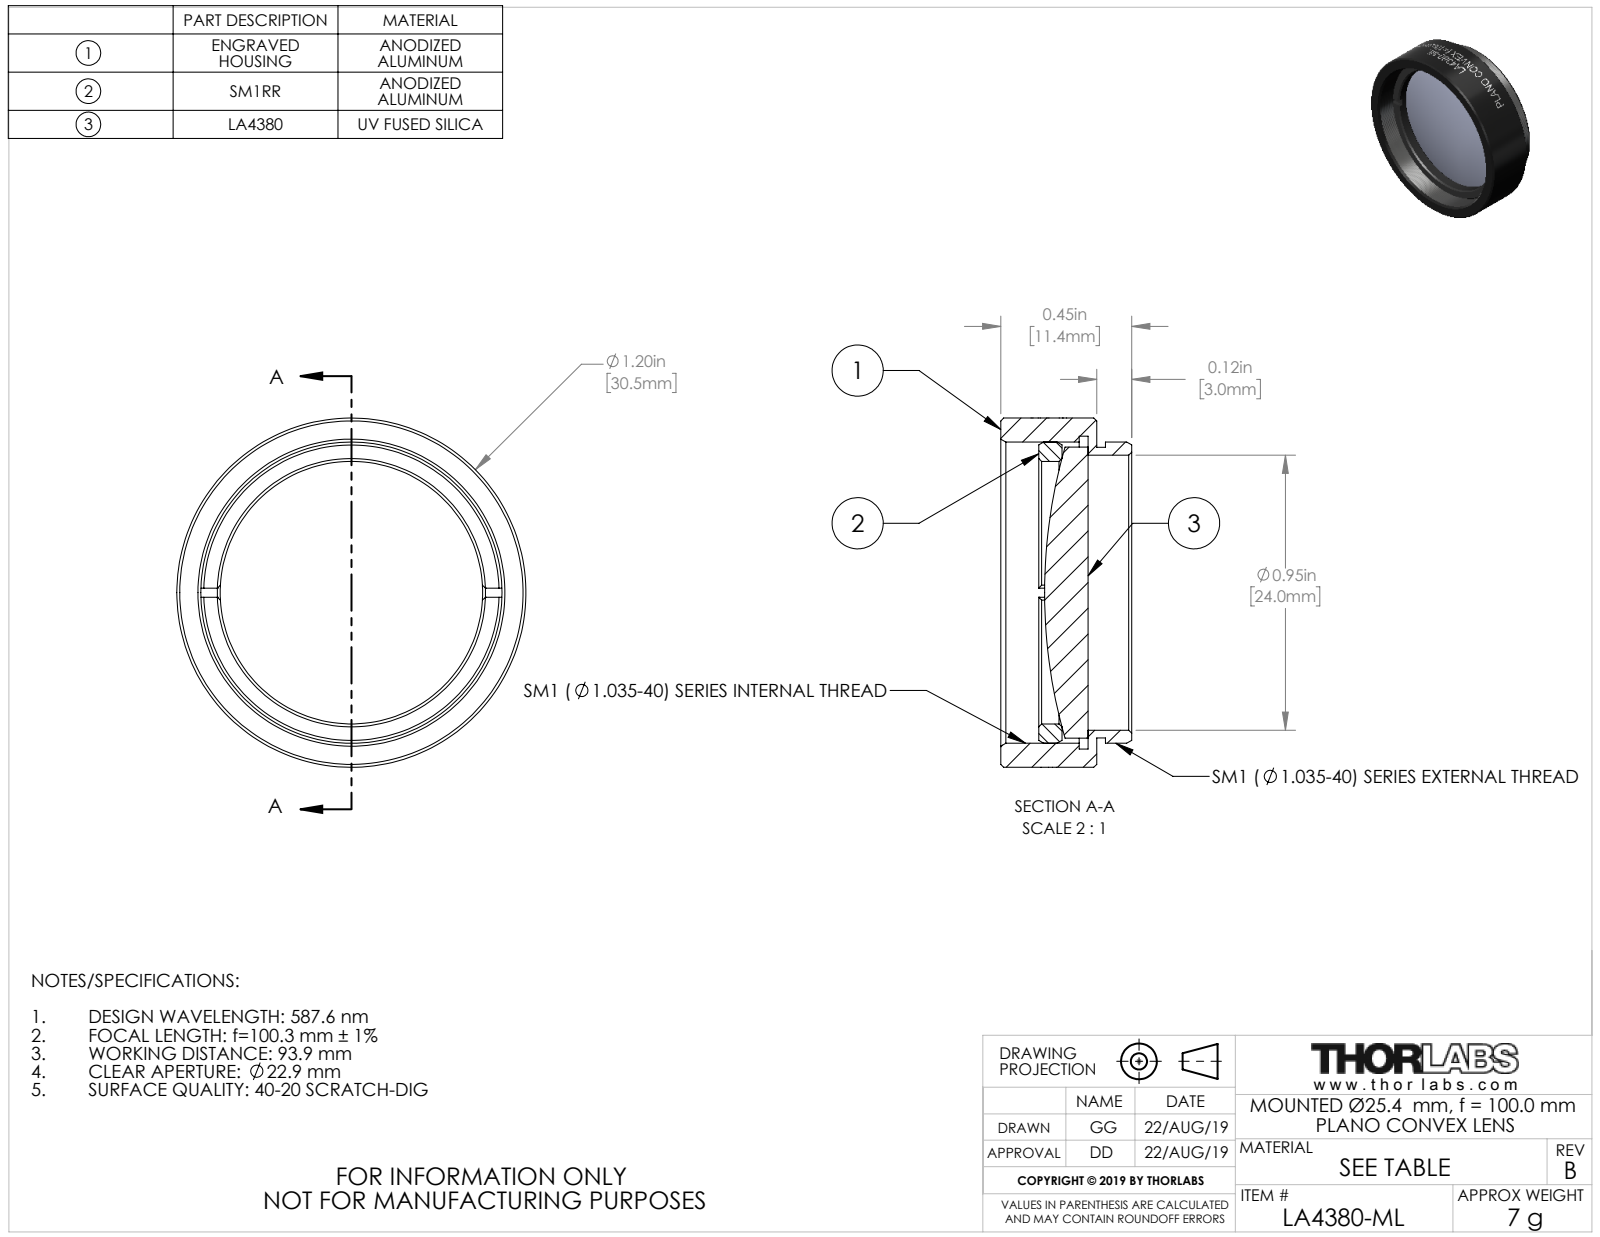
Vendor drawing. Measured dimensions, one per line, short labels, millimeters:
name: 24456-E0W
written by: SolidWorks 2018 (CONFIG_CONTROL_DESIGN)
unit: mm
bodies: 3 solids, 121 faces (20 planar, 77 cylindrical, 24 other)
size: 30.48 × 30.48 × 11.43
volume: 3 551 mm³; area: 4 323 mm²
holes: 1× ⌀22.91, 1× ⌀24, 1× ⌀26.29, 1× ⌀27.3
bosses: 1× ⌀30.48, 1× ⌀26.29, 1× ⌀25.4, 1× ⌀25.37
face distances: 0.76, 8.38, 7.62, 3.03, 2.27, 5.35, 5.06, 4.3, 2.03, 3.32
